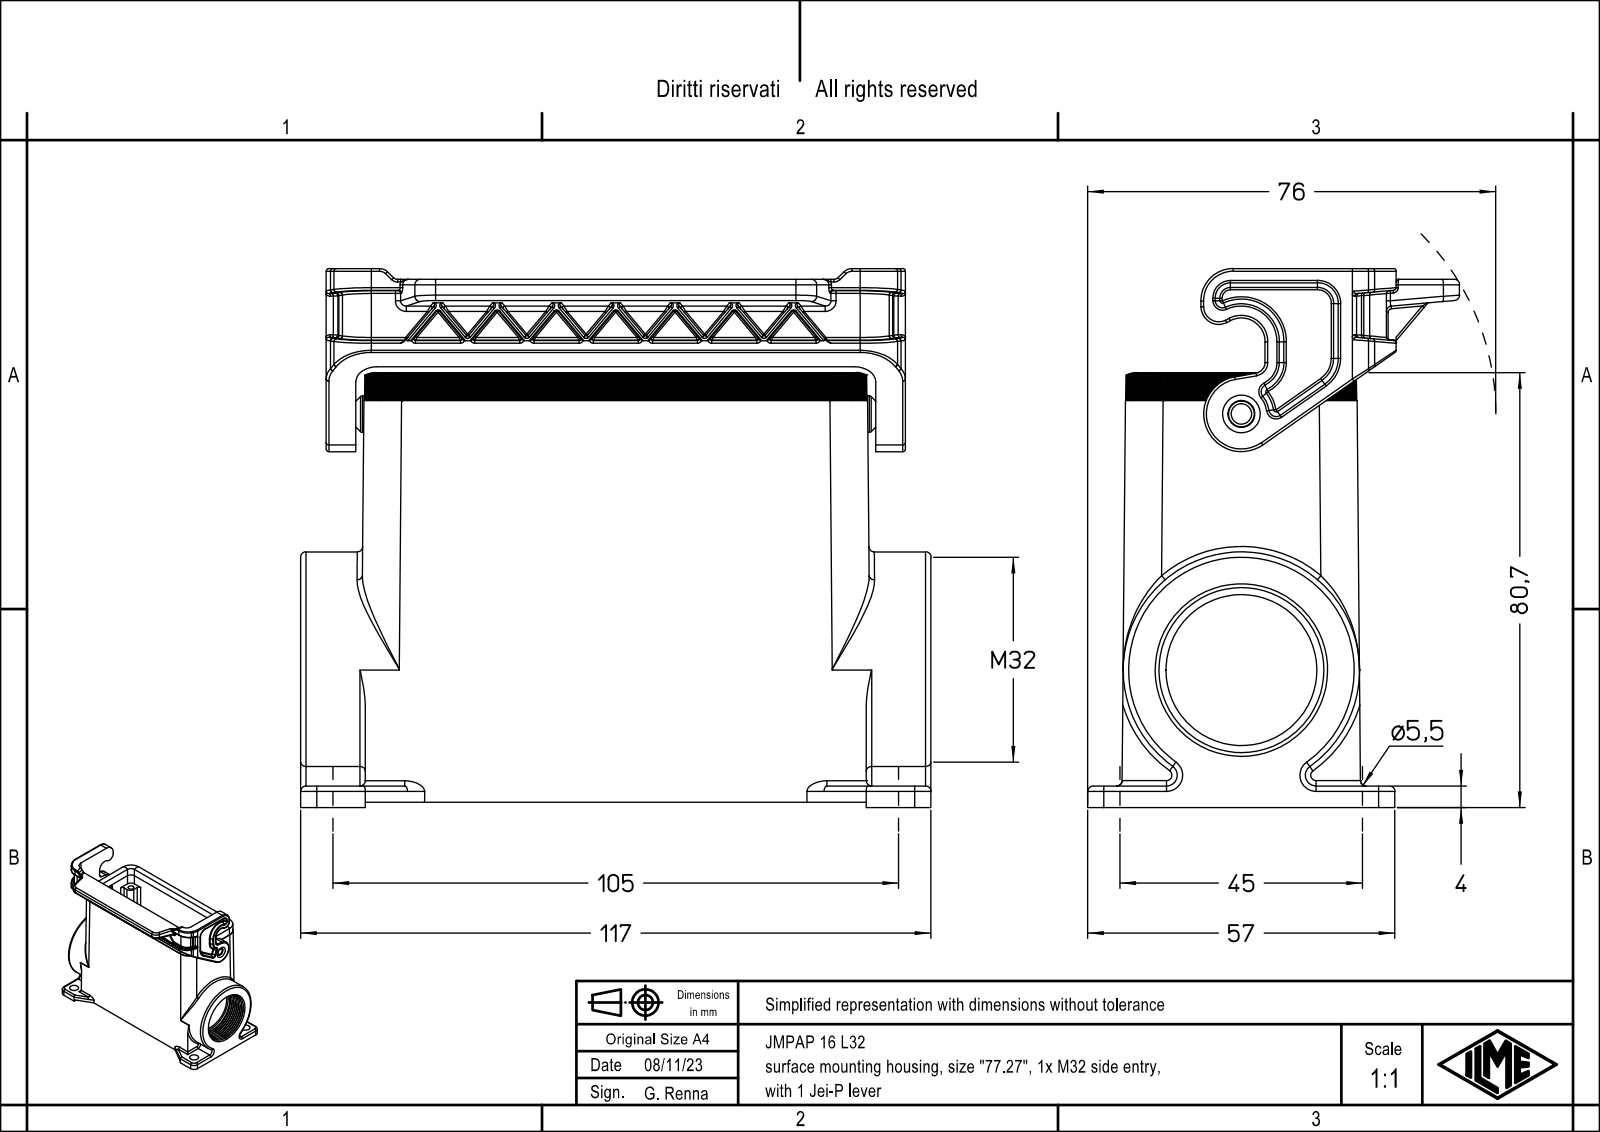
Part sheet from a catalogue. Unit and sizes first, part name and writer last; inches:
Units: inches
Overall size (bounding box): 4.606 × 3.937 × 2.717
Round holes (diameter × count): ⌀0.118 ×4, ⌀0.138 ×4, ⌀0.217 ×3, ⌀0.189 ×1, ⌀1.102 ×1, ⌀1.205 ×1
Round bosses / shafts (diameter × count): ⌀1.727 ×1, ⌀0.268 ×1
Partial cylindrical surfaces — rounded edges, fillets, slot ends (radius × count): R0.012 ×99, R0.02 ×77, R0.039 ×23, R0.118 ×16, R0.079 ×11, R0.276 ×9, R0.059 ×8, R0.157 ×8
Main face-to-face distances: 0.118, 0.039, 0.157, 0.404, 4.203, 3.858, 3.819, 3.701, 0.276, 0.079
Hole centre spacings: 0.647, 1.517, 3.61, 3.862, 1.063, 3.051, 3.231, 1.772
Volume: 9.257 in³ · Surface area: 101.9 in²
Bodies: 1 solid, 849 faces (185 planar, 352 cylindrical, 312 other)
Part name (STEP PRODUCT): JMPAP 16 L32
STEP written by: Creo Elements/Direct Modeling 20.1B 02-Apr-2019 (C) Parametric Technology GmbH (AUTOMOTIVE_DESIGN)
